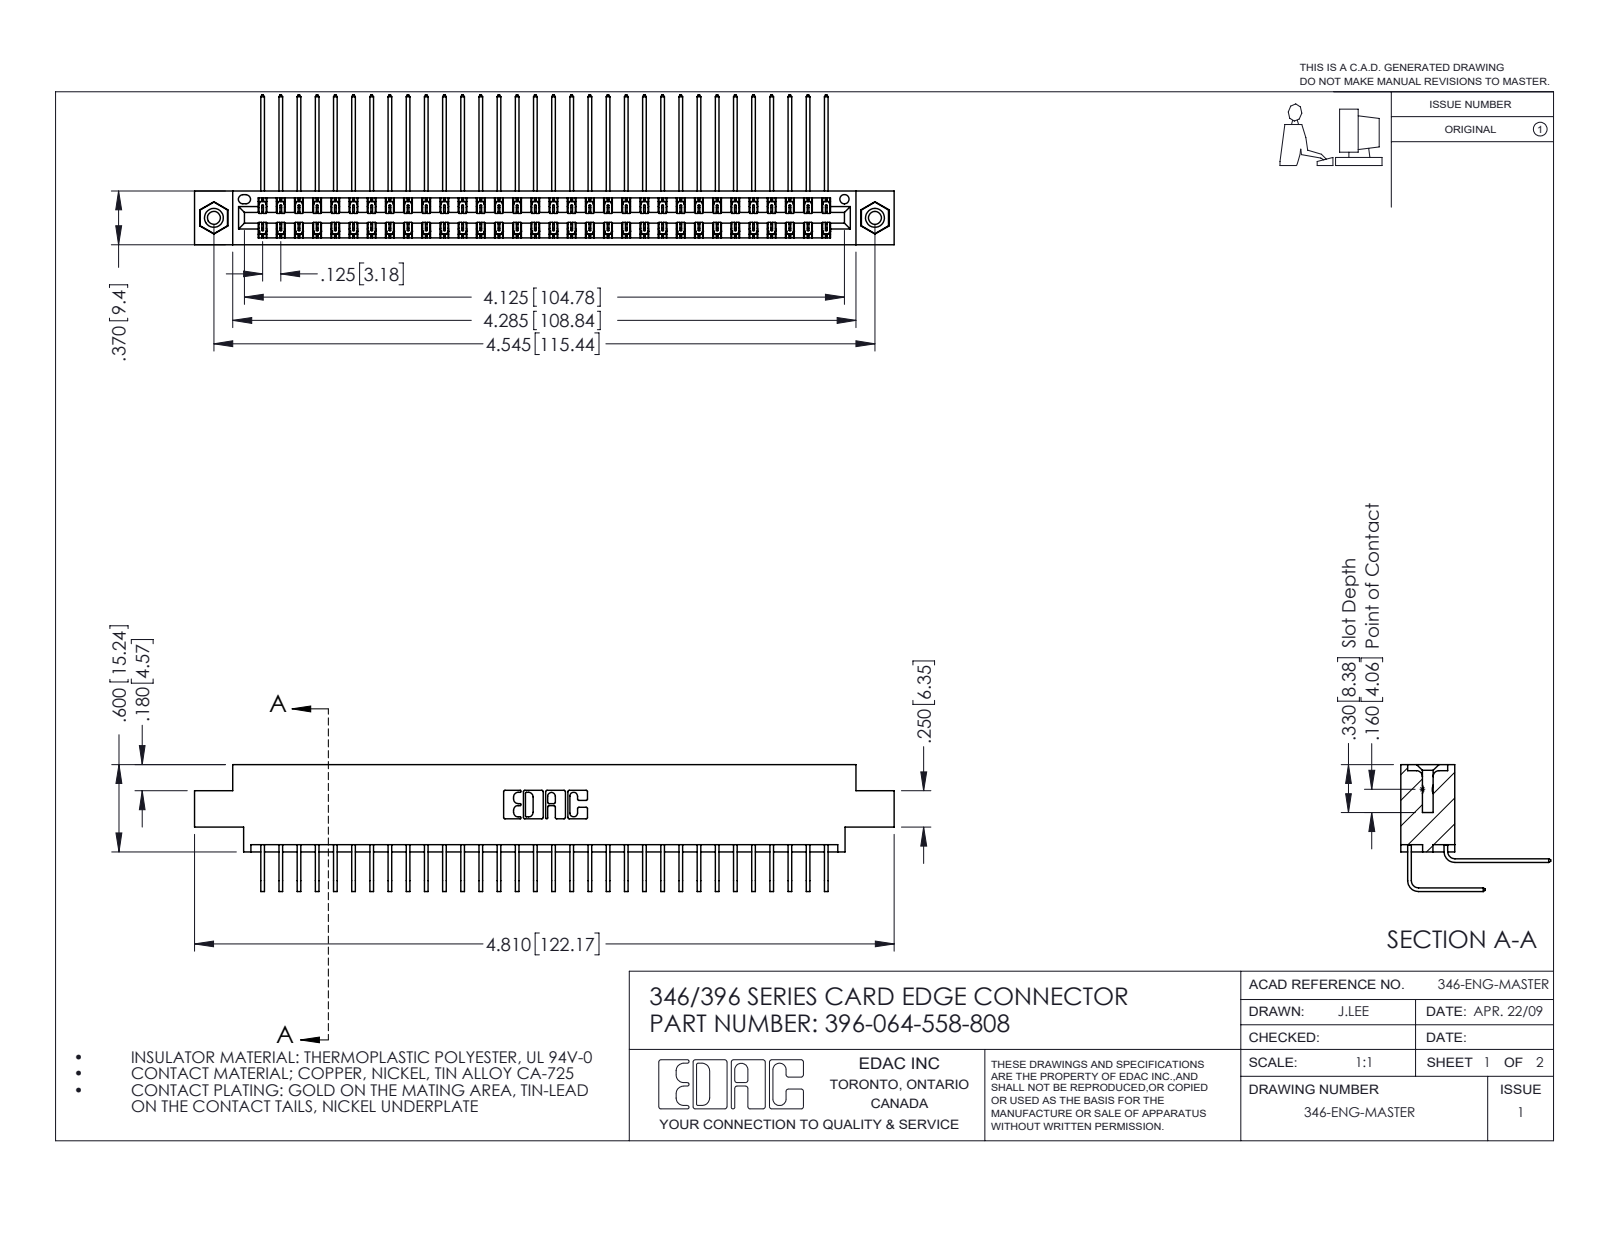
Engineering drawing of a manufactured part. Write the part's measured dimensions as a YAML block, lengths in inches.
part_name: "345-292-001_558 Tail - 2; 345-250-001_345-250-003-102; 396-064-558-808; 346 Part_0.170 Offset - 0.156 Dia-TI (+1 more)"
step_written_by: "SolidWorks 2016 (CONFIG_CONTROL_DESIGN)"
units: inches
bodies: {solids: 67, faces: 3642, planar: 2480, cylindrical: 1146, other: 16}
overall_size: [4.81, 1.03, 0.873]
volume: 0.735
surface_area: 28.47
round_holes:
  - {diameter: 0.089, count: 2}
  - {diameter: 0.125, count: 2}
  - {diameter: 0.156, count: 2}
  - {diameter: 0.064, count: 1}
round_bosses_or_shafts:
  - {diameter: 0.155, count: 2}
partial_cylinders:
  - {radius: 0.006, count: 96}
  - {radius: 0.01, count: 22}
  - {radius: 0.007, count: 6}
  - {radius: 0.031, count: 6}
  - {radius: 0.026, count: 3}
  - {radius: 0.014, count: 2}
  - {radius: 0.022, count: 2}
  - {radius: 0.024, count: 2}
face_to_face_distances: [0.322, 0.048, 0.025, 0.37, 0.25, 0.298, 0.072, 0.275, 0.222, 0.148]
hole_center_spacings: [0.246, 4.337, 4.545]
